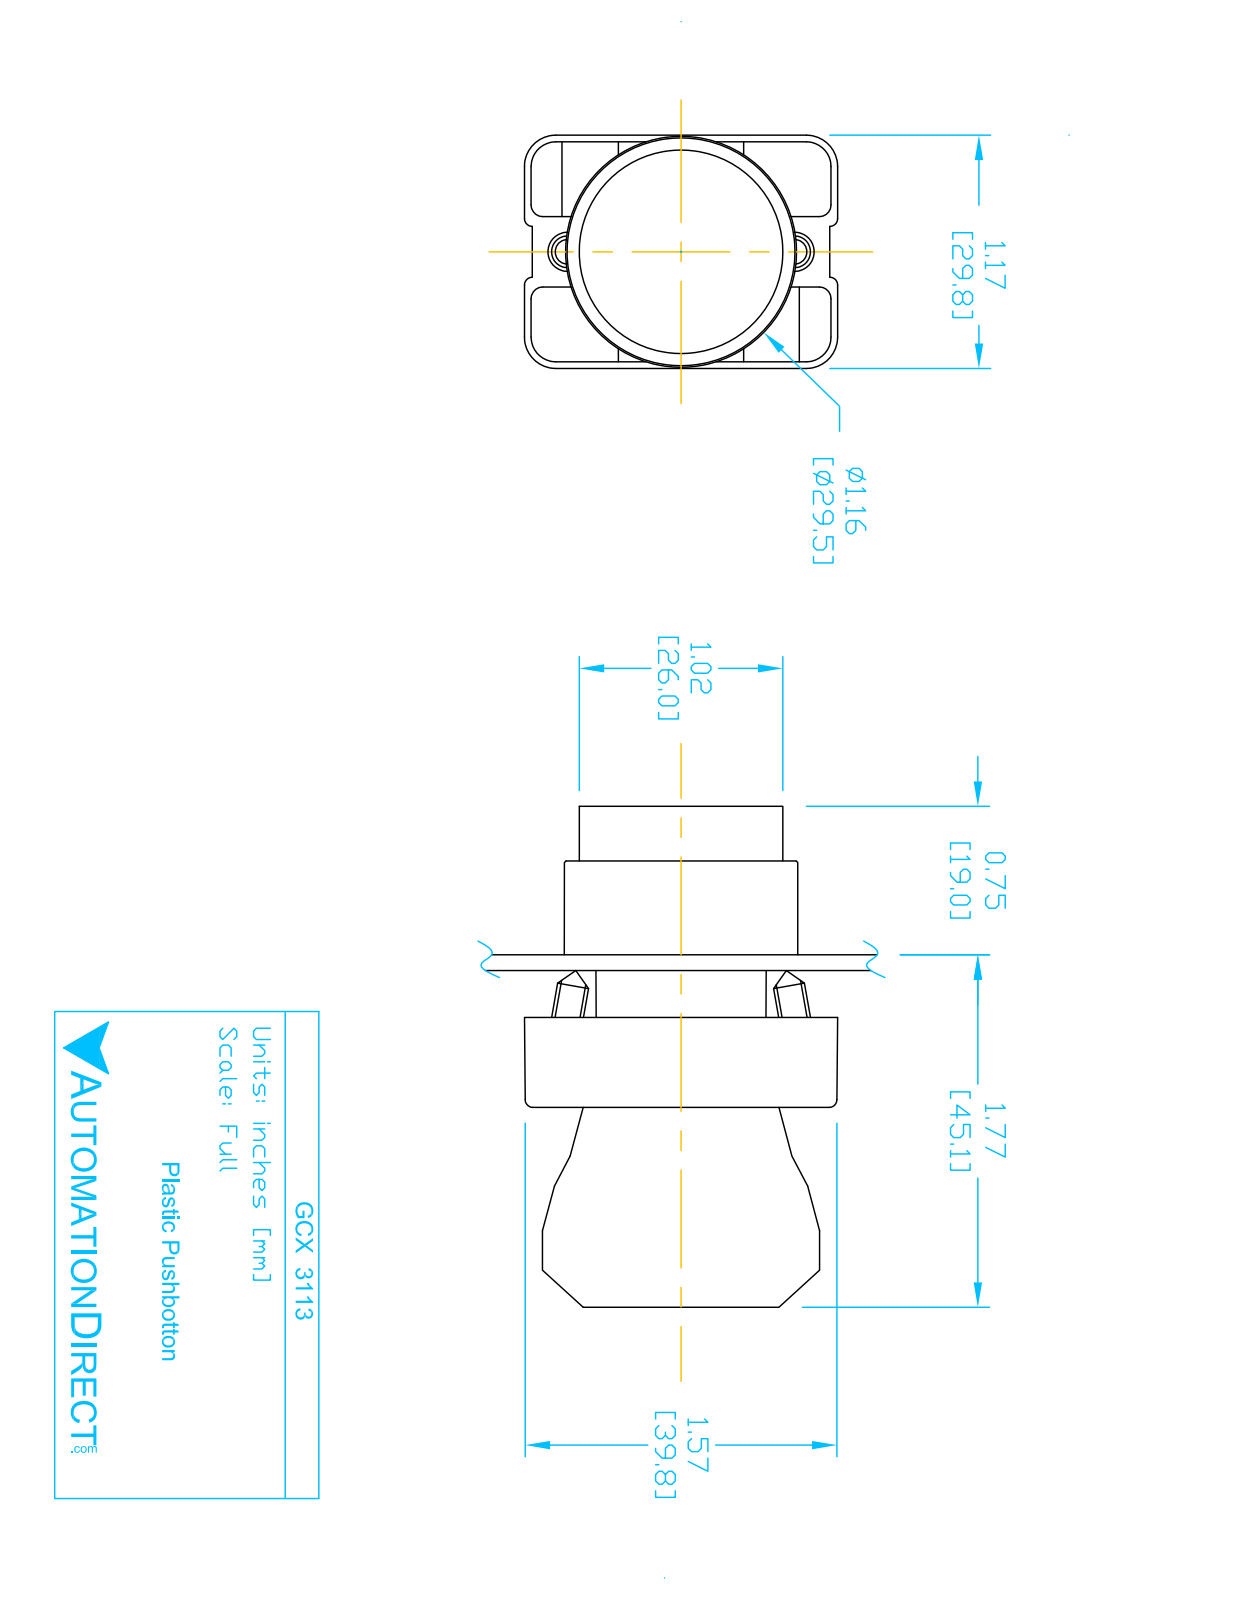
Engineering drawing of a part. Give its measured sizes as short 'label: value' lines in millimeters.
name: GCX3113 OPERATOR; GCX3113; ecx1040; ECX3029-2
written by: SolidWorks 2016 (AUTOMOTIVE_DESIGN)
unit: mm
bodies: 6 solids, 383 faces (222 planar, 132 cylindrical, 29 other)
size: 63.3 × 40.2 × 29.9
volume: 25 960 mm³; area: 17 080 mm²
holes: 2× ⌀2, 2× ⌀3.1, 2× ⌀3.3, 1× ⌀2.2, 1× ⌀5, 1× ⌀22.3, 1× ⌀22.6, 1× ⌀26
bosses: 2× ⌀4, 1× ⌀29.8, 1× ⌀25.5, 1× ⌀24, 1× ⌀21.7, 1× ⌀19.8
rounds: 24× R1.5, 12× R1, 12× R3.1, 12× R4, 4× R1, 2× R3.3, 1× R0.5, 1× R1.6
face distances: 14.7, 0.8, 30.3, 0.8, 12, 18.3, 7, 17.5, 15.2, 29.5
hole spacings: 6, 13.8, 12, 12.4
